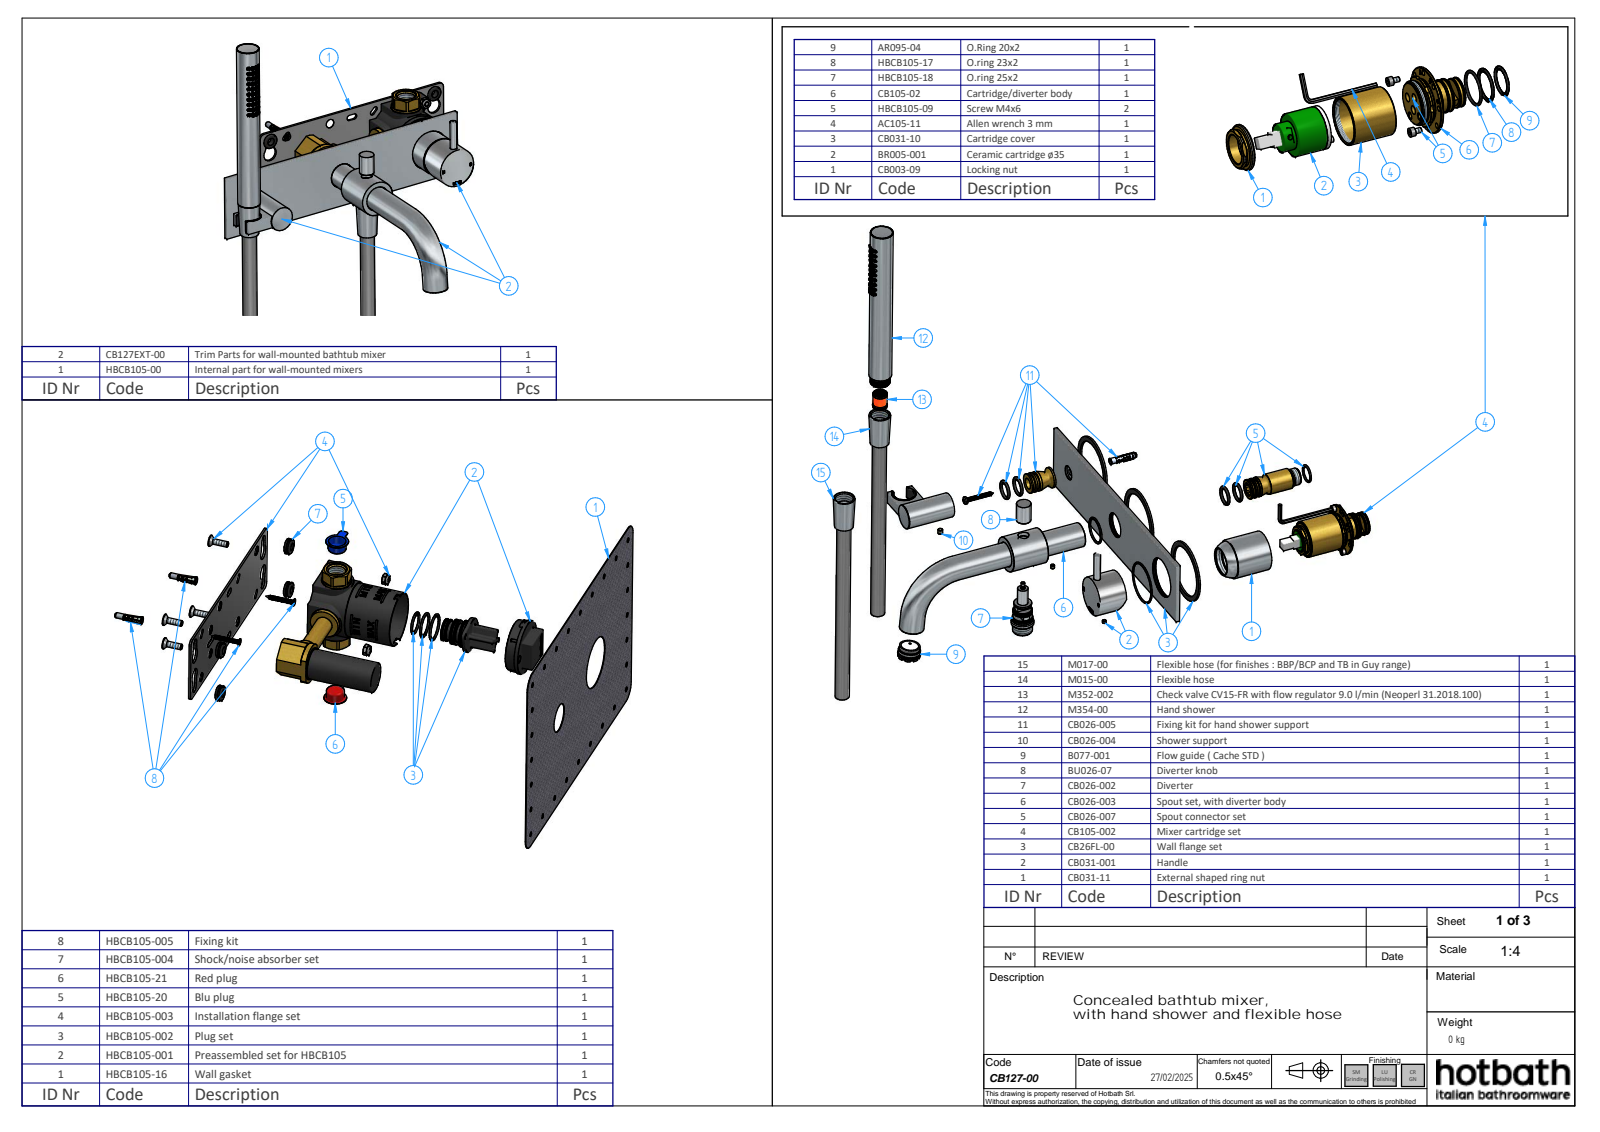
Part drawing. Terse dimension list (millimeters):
name: CB127EXT-00; CB031-11; CB031-001_oa_0; CB031-12 (+8 more)
written by: Solid Edge (AUTOMOTIVE_DESIGN)
unit: mm
bodies: 18 solids, 1386 faces (411 planar, 384 cylindrical, 591 other)
size: 464.85 × 298.22 × 210.05
volume: 285 702 mm³; area: 194 048 mm²
holes: 40× ⌀3.2, 4× ⌀3.24, 3× ⌀23, 3× ⌀66.5, 2× ⌀5, 2× ⌀15, 2× ⌀16.5, 2× ⌀18.63, 2× ⌀21.2, 2× ⌀22.2, 2× ⌀22.92, 2× ⌀24.2
bosses: 4× ⌀24, 3× ⌀50.5, 3× ⌀26, 2× ⌀15, 1× ⌀42, 1× ⌀38, 1× ⌀23.47, 1× ⌀22.8
rounds: 53× R0.2, 7× R0.5, 6× R5, 4× R0.35, 4× R1, 3× R0.59, 2× R0.22, 2× R0.23
face distances: 4, 2.3, 1.7, 70, 9.2, 13.9, 16.2, 50.5, 52.8, 54.5
hole spacings: 7.21, 6, 12, 12.65, 18.44, 4, 18, 24.33
